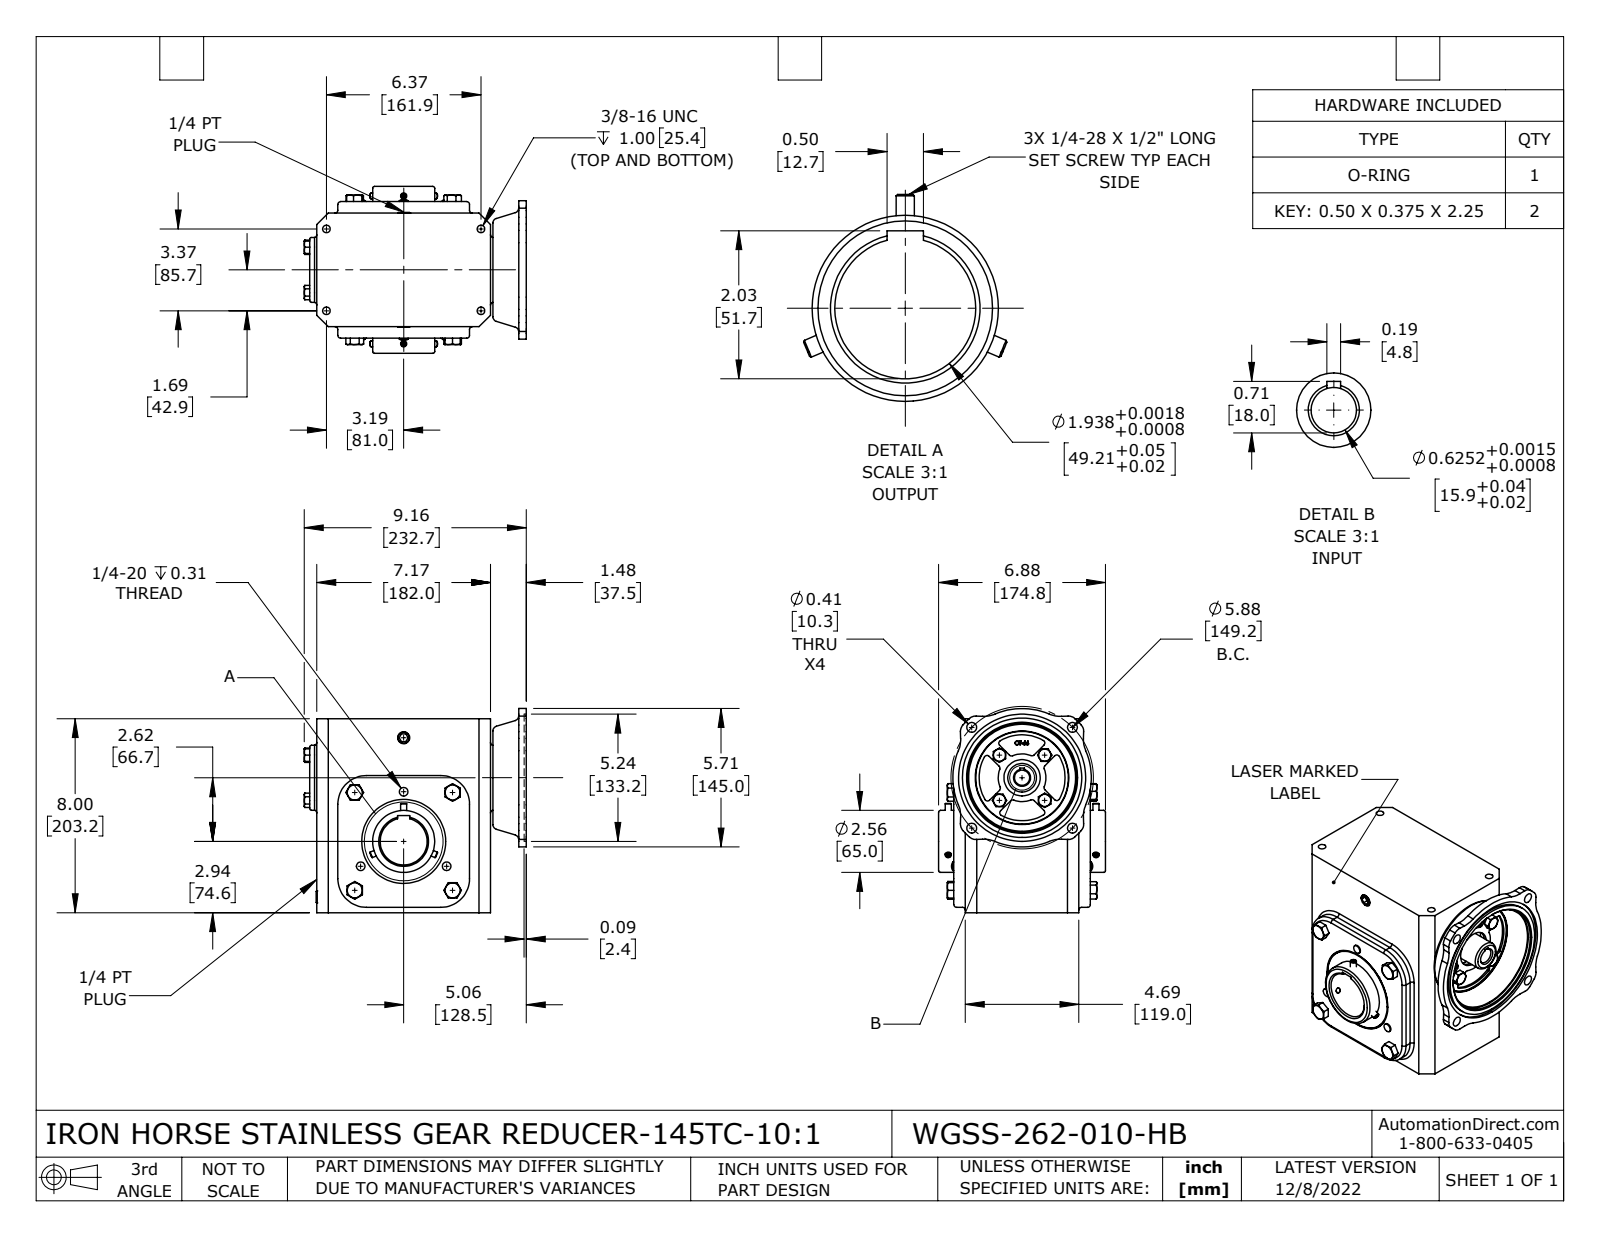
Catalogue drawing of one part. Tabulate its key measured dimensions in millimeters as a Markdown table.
| quantity | value |
| --- | --- |
| part name | WGSS-262-010-HB |
| STEP written by | SolidWorks 2021 (CONFIG_CONTROL_DESIGN) |
| units | millimeters |
| bodies | 7 solids, 669 faces (285 planar, 191 cylindrical, 193 other) |
| overall size | 232.7 × 213.8 × 174.8 |
| volume | 4 738 000 mm³ |
| surface area | 273 300 mm² |
| round holes (diameter × count) | 5.4 × 6, 8 × 4, 10.3 × 4, 15.9 × 1, 22 × 1, 38 × 1, 45 × 1, 49.2 × 1, 52 × 1, 97 × 1, 114.3 × 1, 133.2 × 1 |
| round bosses / shafts (diameter × count) | 6.4 × 6, 9 × 3, 125 × 1, 88 × 1, 65 × 1, 30 × 1 |
| partial cylindrical surfaces (radius × count) | 3 × 40, 10 × 12, 30 × 12, 2 × 4, 25 × 1, 45 × 1, 72.5 × 1, 83.1 × 1 |
| main face-to-face distances | 12, 131, 203.2, 182, 119, 143, 189.5, 195.8, 7.5, 29.5 |
| hole center spacings | 74.6, 88, 105.5, 145, 154.8, 85.7, 149.2, 161.9 |
